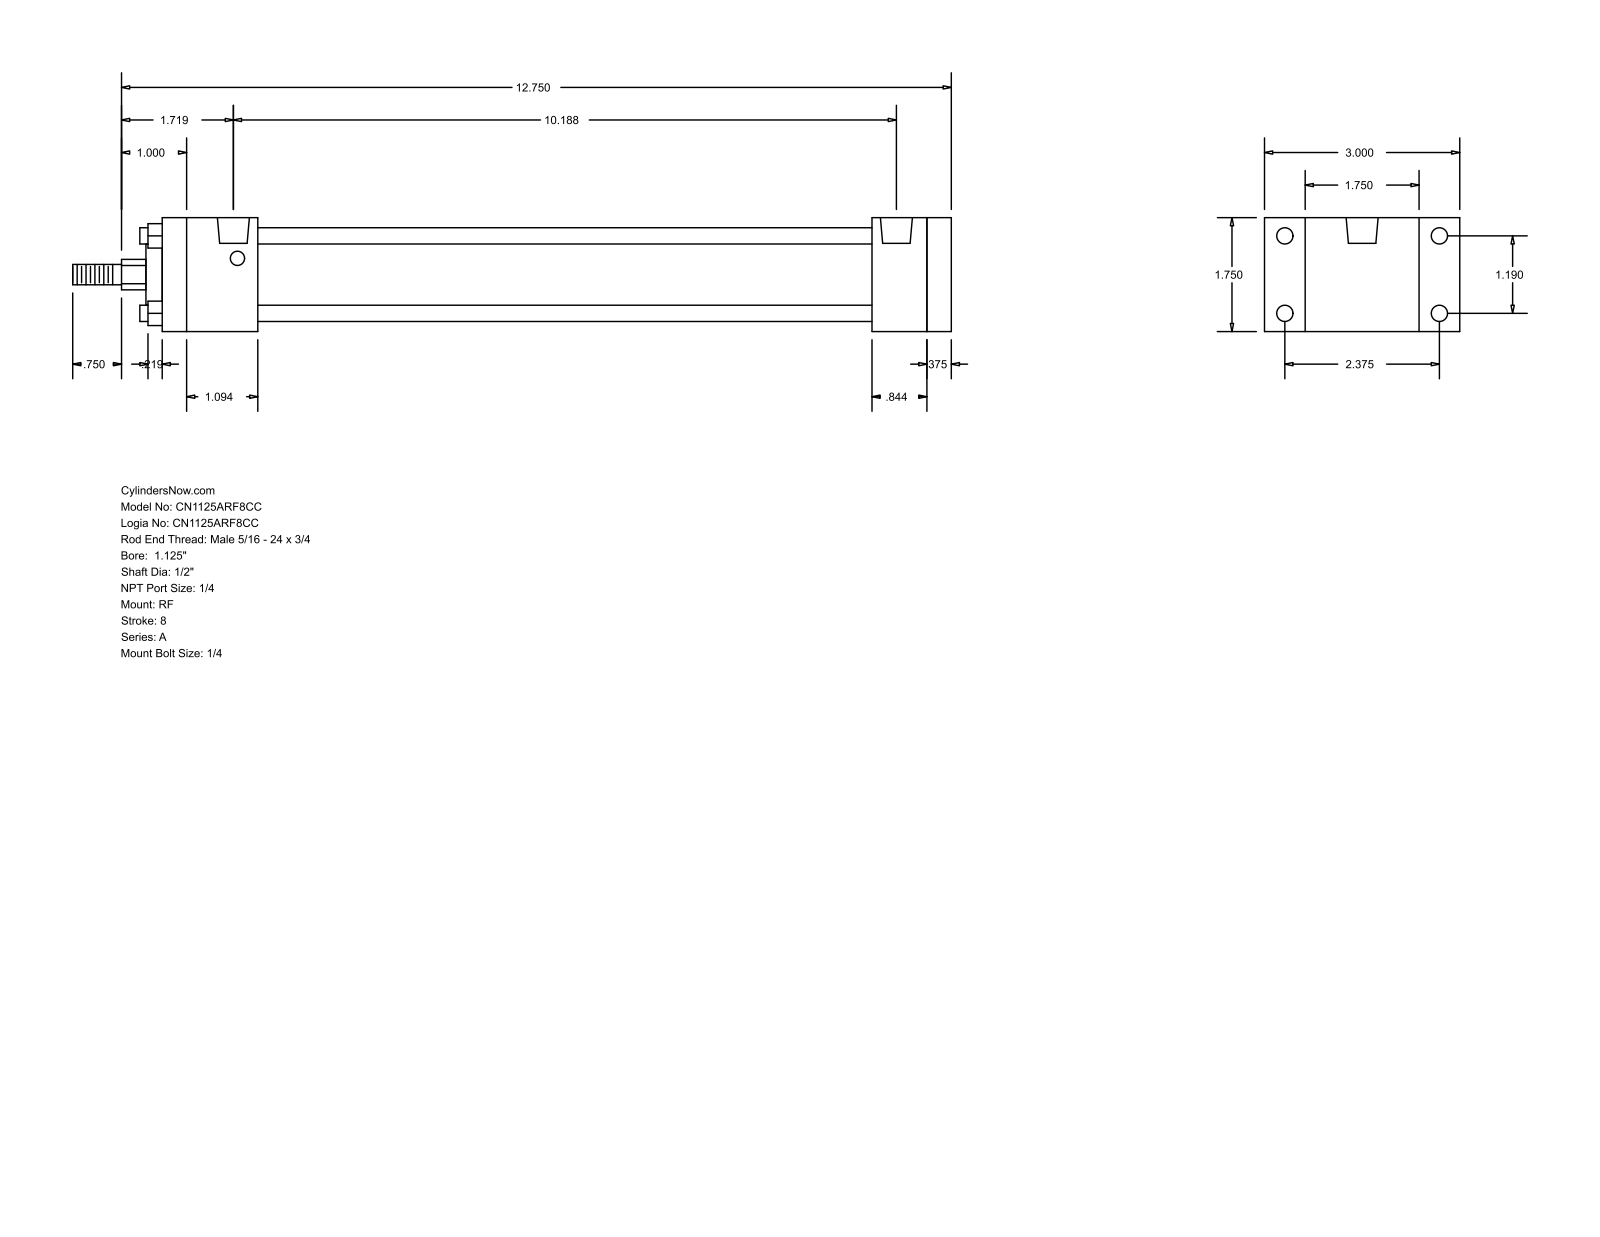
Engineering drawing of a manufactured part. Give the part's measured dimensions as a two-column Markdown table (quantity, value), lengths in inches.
| quantity | value |
| --- | --- |
| part name | A_RF__0112_0.5 |
| STEP written by | GSSL Pune (CONFIG_CONTROL_DESIGN) |
| units | inches |
| bodies | 0 solids, 92 faces (64 planar, 28 cylindrical, 0 other) |
| overall size | 13.5 × 3 × 1.75 |
| round holes (diameter × count) | 0.219 × 4, 0.25 × 4, 0.492 × 2 |
| round bosses / shafts (diameter × count) | 0.25 × 4, 1.255 × 1, 0.937 × 1, 0.5 × 1, 0.313 × 1 |
| partial cylindrical surfaces (radius × count) | 0.234 × 1 |
| main face-to-face distances | 1.75, 0.375, 12.125, 11.75, 1.469, 10.906, 9.437, 10.281, 10.656, 0.844 |
| hole center spacings | 1.19, 2.375, 2.656, 10.063, 0.062, 0.063, 10.125, 10.125 |
